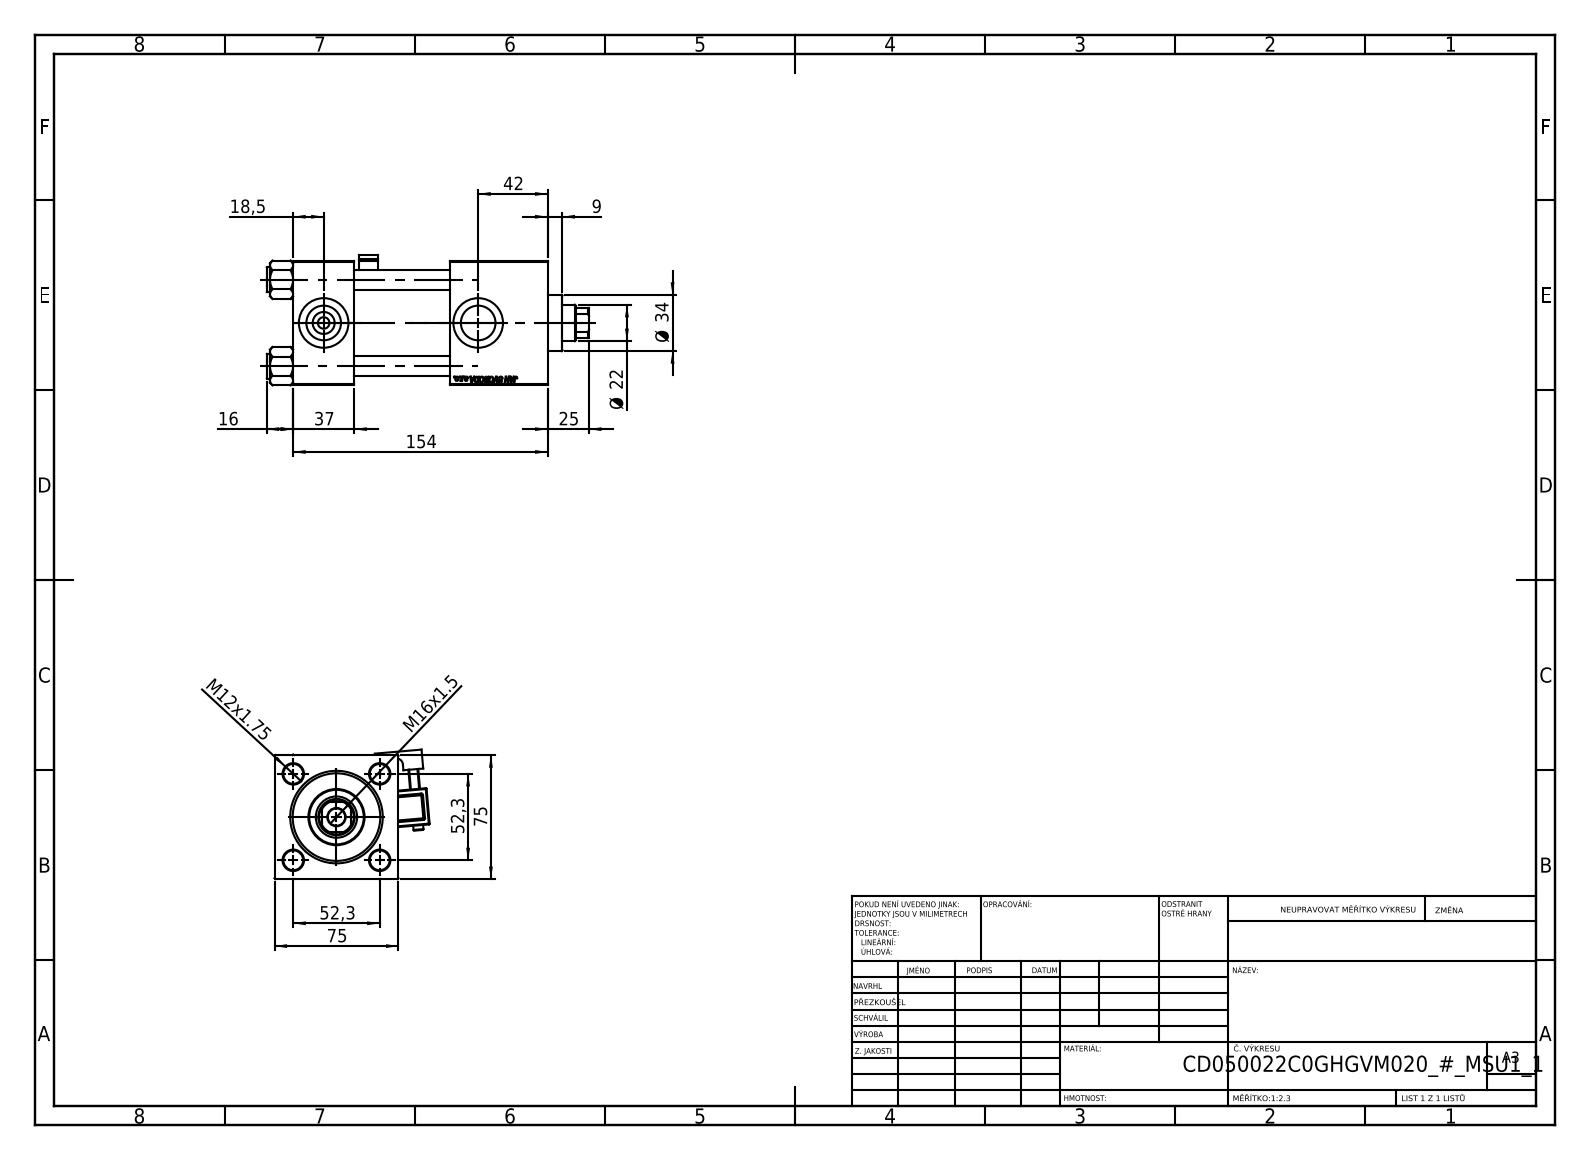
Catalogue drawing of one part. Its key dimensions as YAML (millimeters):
part_name: "NUT_M5_V215CD_C; V215CD_VC_C; V215CD_C_TYCINKA; V215CR_MSU (+2 more)"
step_written_by: "SolidWorks 2019 (CONFIG_CONTROL_DESIGN)"
units: millimeters
bodies: {solids: 12, faces: 1225, planar: 555, cylindrical: 116, other: 554}
overall_size: [195, 93.85, 78.61]
volume: 677537
surface_area: 153420
round_holes:
  - {diameter: 12, count: 4}
  - {diameter: 7, count: 2}
  - {diameter: 20.96, count: 2}
  - {diameter: 30, count: 2}
  - {diameter: 10.5, count: 1}
  - {diameter: 22, count: 1}
  - {diameter: 25, count: 1}
  - {diameter: 41, count: 1}
  - {diameter: 50, count: 1}
  - {diameter: 53, count: 1}
round_bosses_or_shafts:
  - {diameter: 15, count: 4}
  - {diameter: 56, count: 1}
  - {diameter: 34, count: 1}
  - {diameter: 6, count: 1}
partial_cylinders:
  - {radius: 0.5, count: 24}
  - {radius: 1, count: 1}
  - {radius: 2.5, count: 1}
  - {radius: 4, count: 1}
  - {radius: 10.5, count: 1}
face_to_face_distances: [75, 37, 154, 117, 95, 58, 59, 125.3, 88.3, 30.3]
hole_center_spacings: [36.98, 52.3, 73.96, 93.5]
